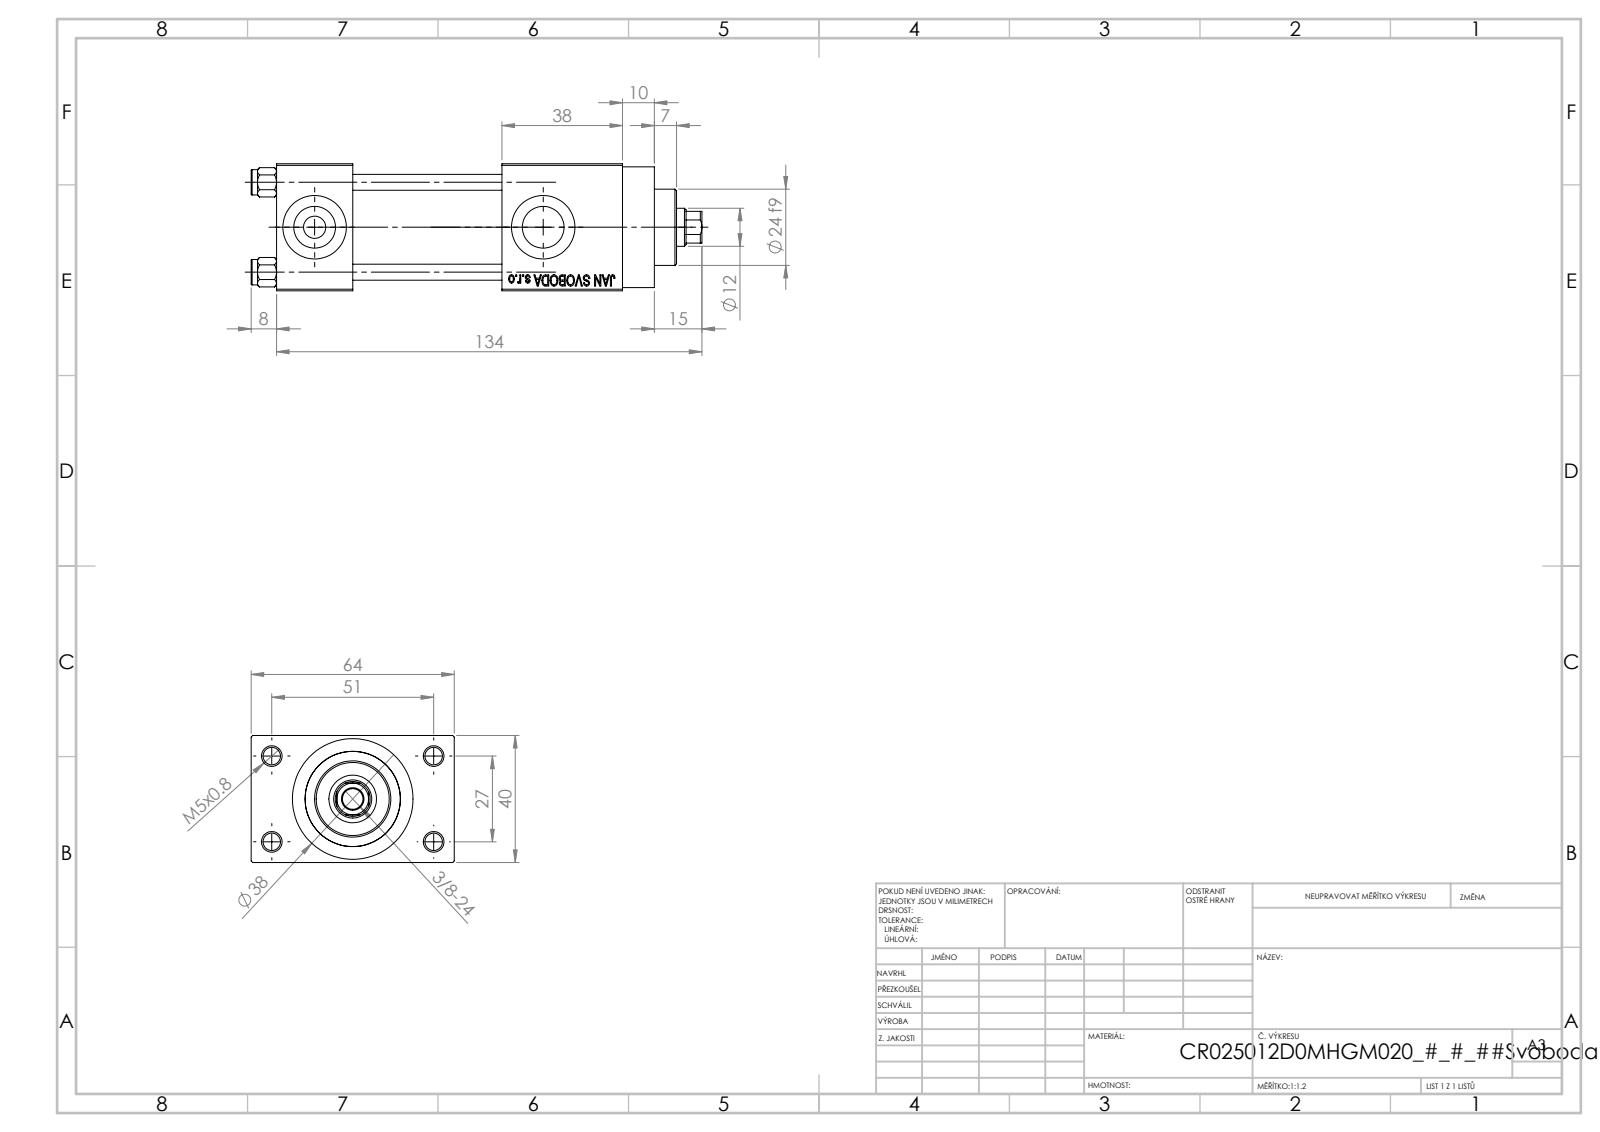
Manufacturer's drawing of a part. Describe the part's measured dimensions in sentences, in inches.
The part is named "V215_VC_A; V215CR_VCP_D; NUT_M5_D; V215CR_D_TYCINKA (+1 more)". Its 3-D file was written by "SolidWorks 2019 (CONFIG_CONTROL_DESIGN)". It is 11 solids with 1102 faces: 496 planar, 88 cylindrical and 518 other. Overall it measures 5.591 by 2.52 by 1.575 inches. Its volume is 10.6 cubic inches and its surface area 96.35 square inches. Round holes: 4 of diameter 0.197, 4 of diameter 0.217, 3 of diameter 0.787, 2 of diameter 0.276, 2 of diameter 0.518, 1 of diameter 0.256, 1 of diameter 0.472, 1 of diameter 0.591, 1 of diameter 0.984, 1 of diameter 1.181. Round bosses or shafts: 4 of diameter 0.315, 1 of diameter 1.496, 1 of diameter 1.22, 1 of diameter 0.945. Partial cylindrical surfaces (rounded edges, fillets, slot ends): 1 of radius 0.217. The main face-to-face distances are 1.575, 0.472, 1.85, 0.945, 2.795, 2.047, 1.496, 4.291, 3.346, 2.52. The hole center spacings are 0.448, 0.788, 1.114, 1.136, 1.177, 1.561, 1.903, 1.063.
